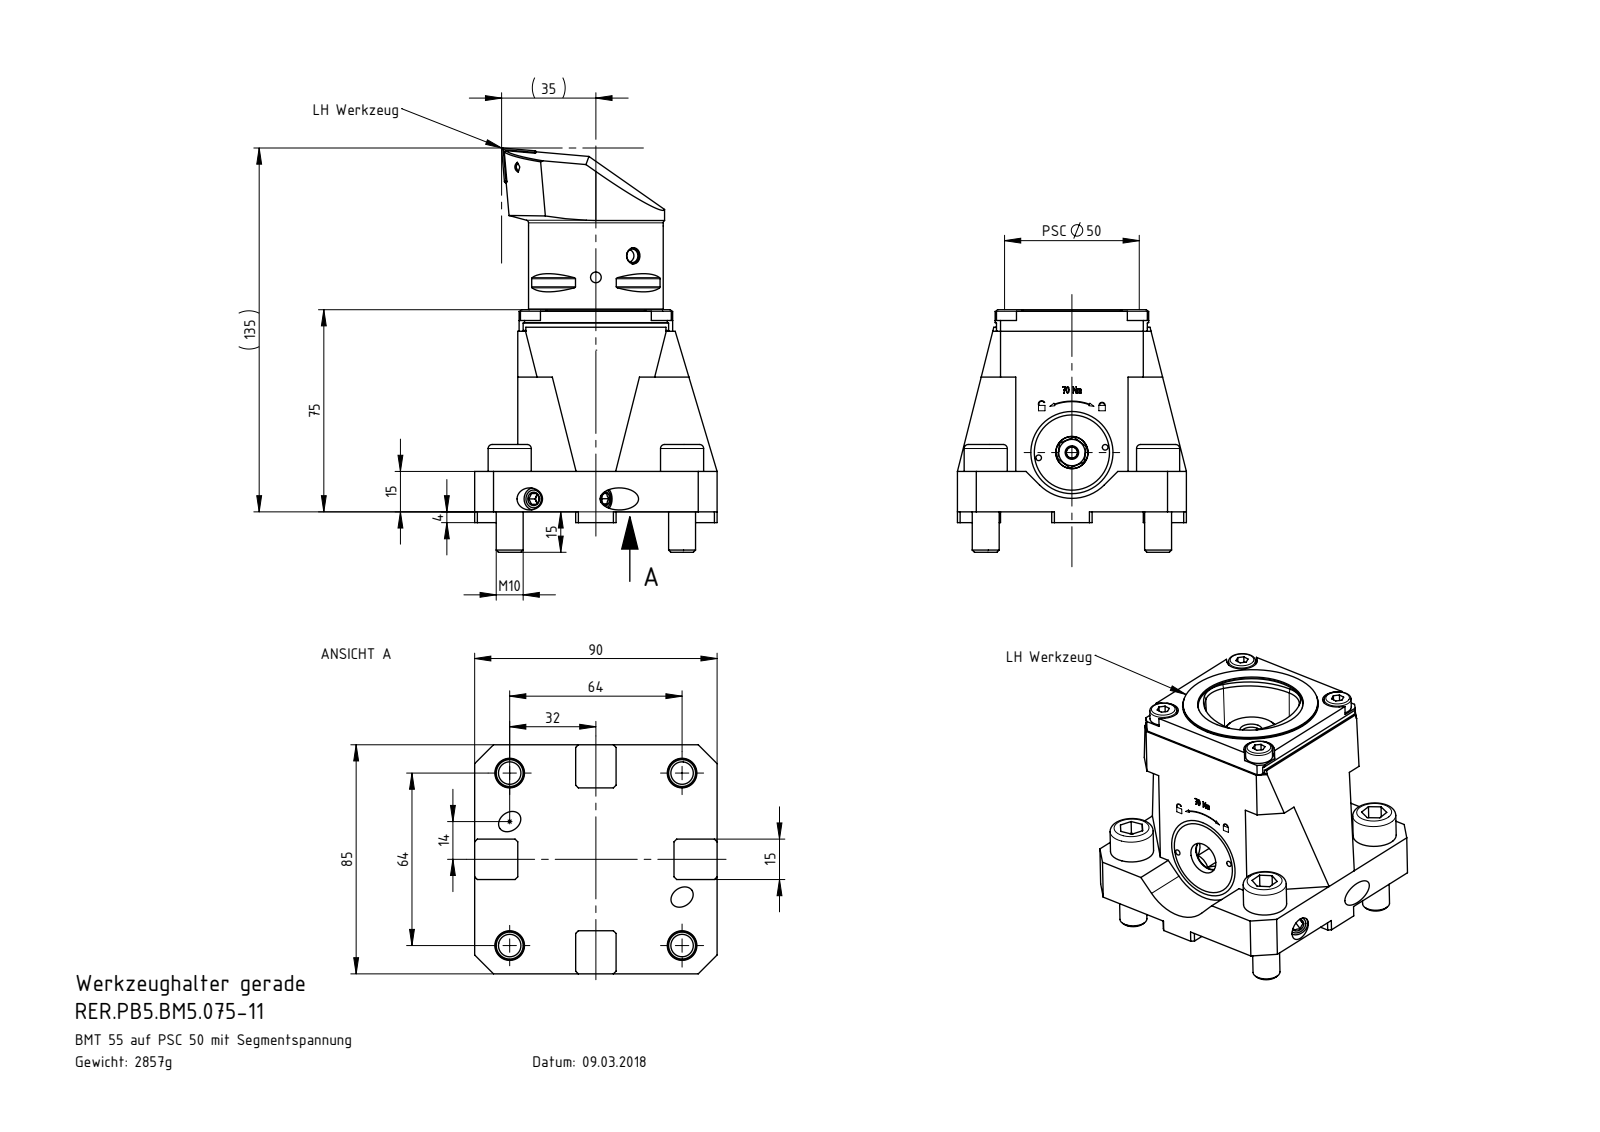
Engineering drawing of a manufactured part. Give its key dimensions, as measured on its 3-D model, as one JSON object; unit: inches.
{"part_name": "O-Ring_1.50-AD15.00; RER-PB5.BM5.075-11_B; O-Ring_1.50-AD31.50; ISO 4026 - M5 x 5 (+8 more)", "step_written_by": "SolidWorks 2017 (AUTOMOTIVE_DESIGN)", "units": "inches", "bodies": {"solids": 36, "faces": 1040, "planar": 493, "cylindrical": 216, "other": 331}, "overall_size": [3.543, 3.543, 3.346], "volume_in3": 18.99, "surface_area_in2": 169.8, "round_holes": [[0.268, 5], [0.165, 4], [0.197, 4], [0.244, 4], [0.433, 4], [0.083, 3], [0.118, 3], [0.323, 3], [0.13, 2], [0.164, 2], [0.276, 1], [0.28, 1]], "round_bosses_or_shafts": [[0.394, 8], [0.63, 4], [0.236, 4], [0.315, 3], [0.276, 2], [0.157, 2], [1.969, 1], [1.957, 1]], "partial_cylinders_radius": [[0.012, 12], [0.197, 4], [0.22, 4], [0.008, 2], [0.157, 2], [0.159, 2], [0.161, 2], [0.433, 1]], "face_to_face_distances": [0.157, 1.102, 0.591, 2.047, 2.638, 0.945, 1.85, 1.26, 2.795, 2.775], "hole_center_spacings": [2.194, 0.501, 1.281, 1.781, 1.811, 2.52, 3.062, 0.492]}
